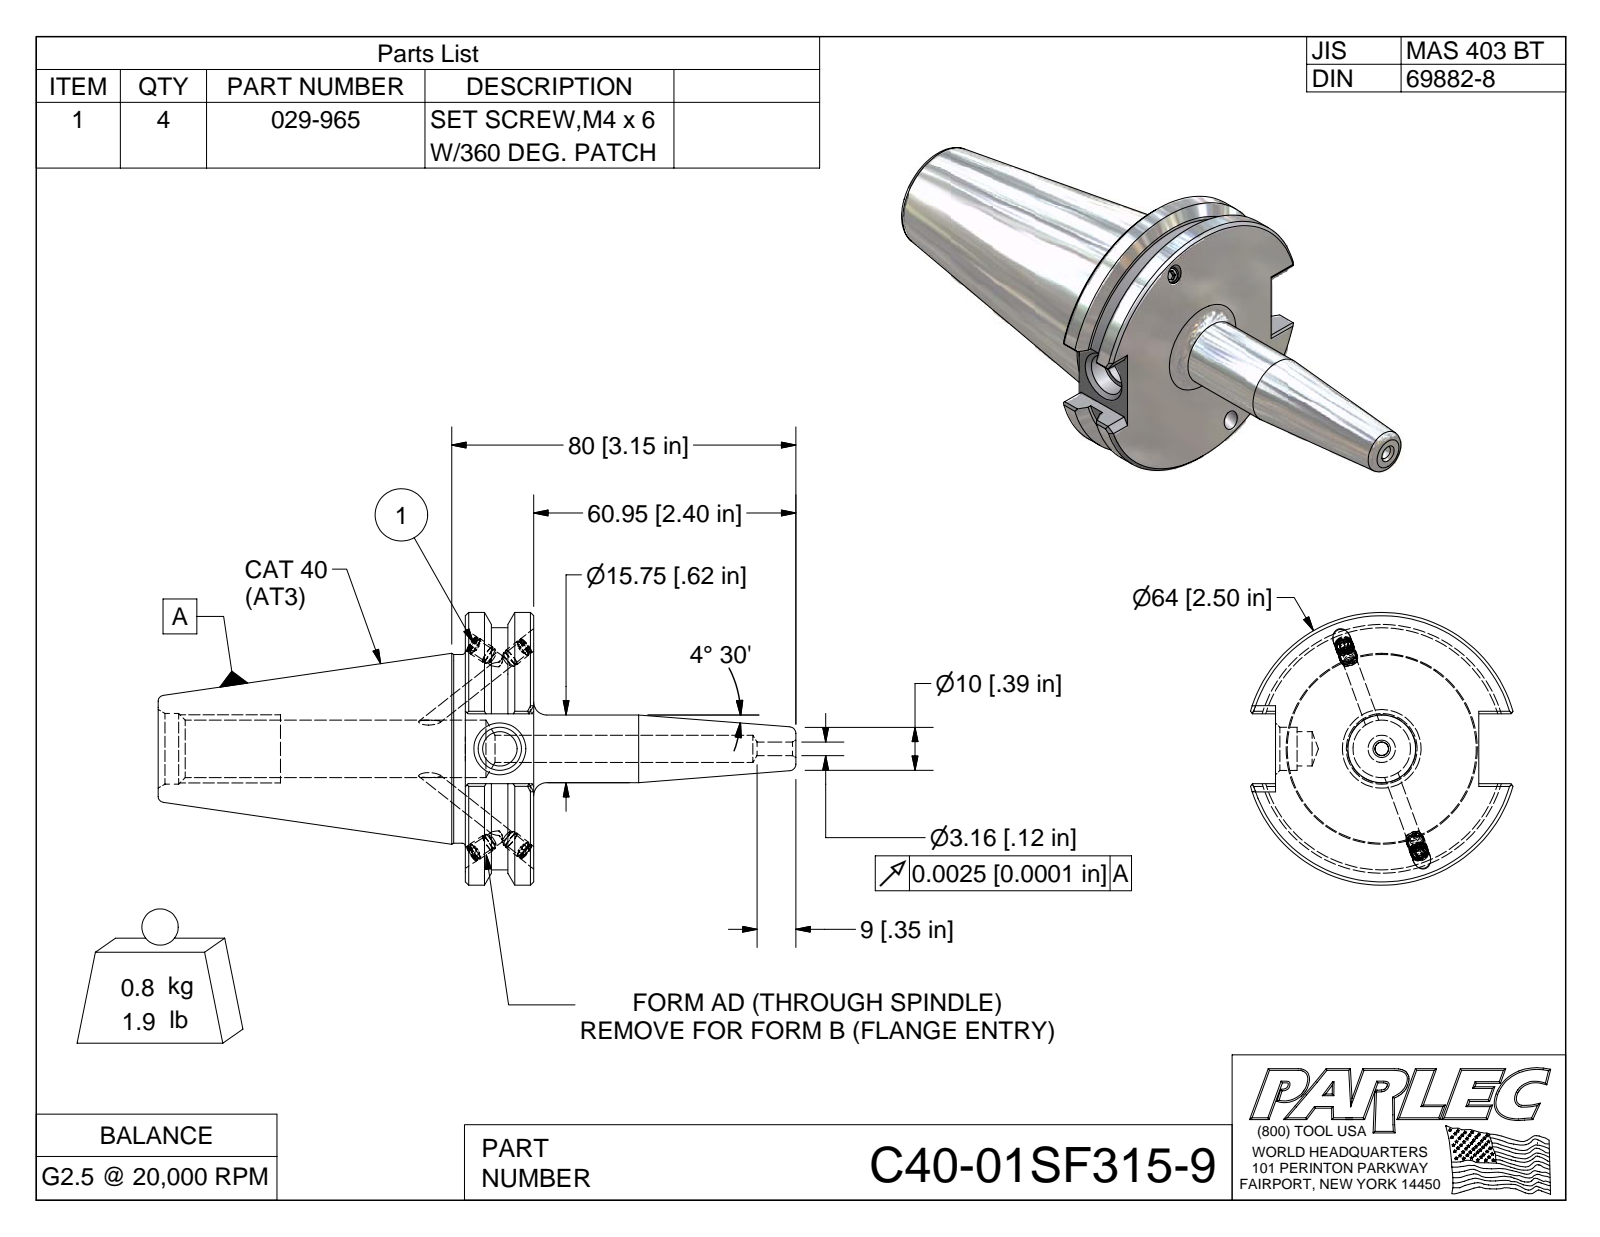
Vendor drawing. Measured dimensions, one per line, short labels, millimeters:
name: C40-01SF315-9; C40BC-01SF315-9-1; 029-965
written by: Autodesk Inventor 2009 (AUTOMOTIVE_DESIGN)
unit: mm
bodies: 5 solids, 150 faces (76 planar, 29 cylindrical, 45 other)
size: 148.3 × 63.5 × 61
volume: 109 000 mm³; area: 25 010 mm²
holes: 4× ⌀3.3, 4× ⌀4.1, 1× ⌀3.1
bosses: 4× ⌀4.2, 4× ⌀4, 1× ⌀63.5, 1× ⌀56.4, 1× ⌀43.9, 1× ⌀15.7
face distances: 15.9, 16.3, 47.2, 71.4, 87.3, 81.3, 9.9, 6, 77.5, 6
